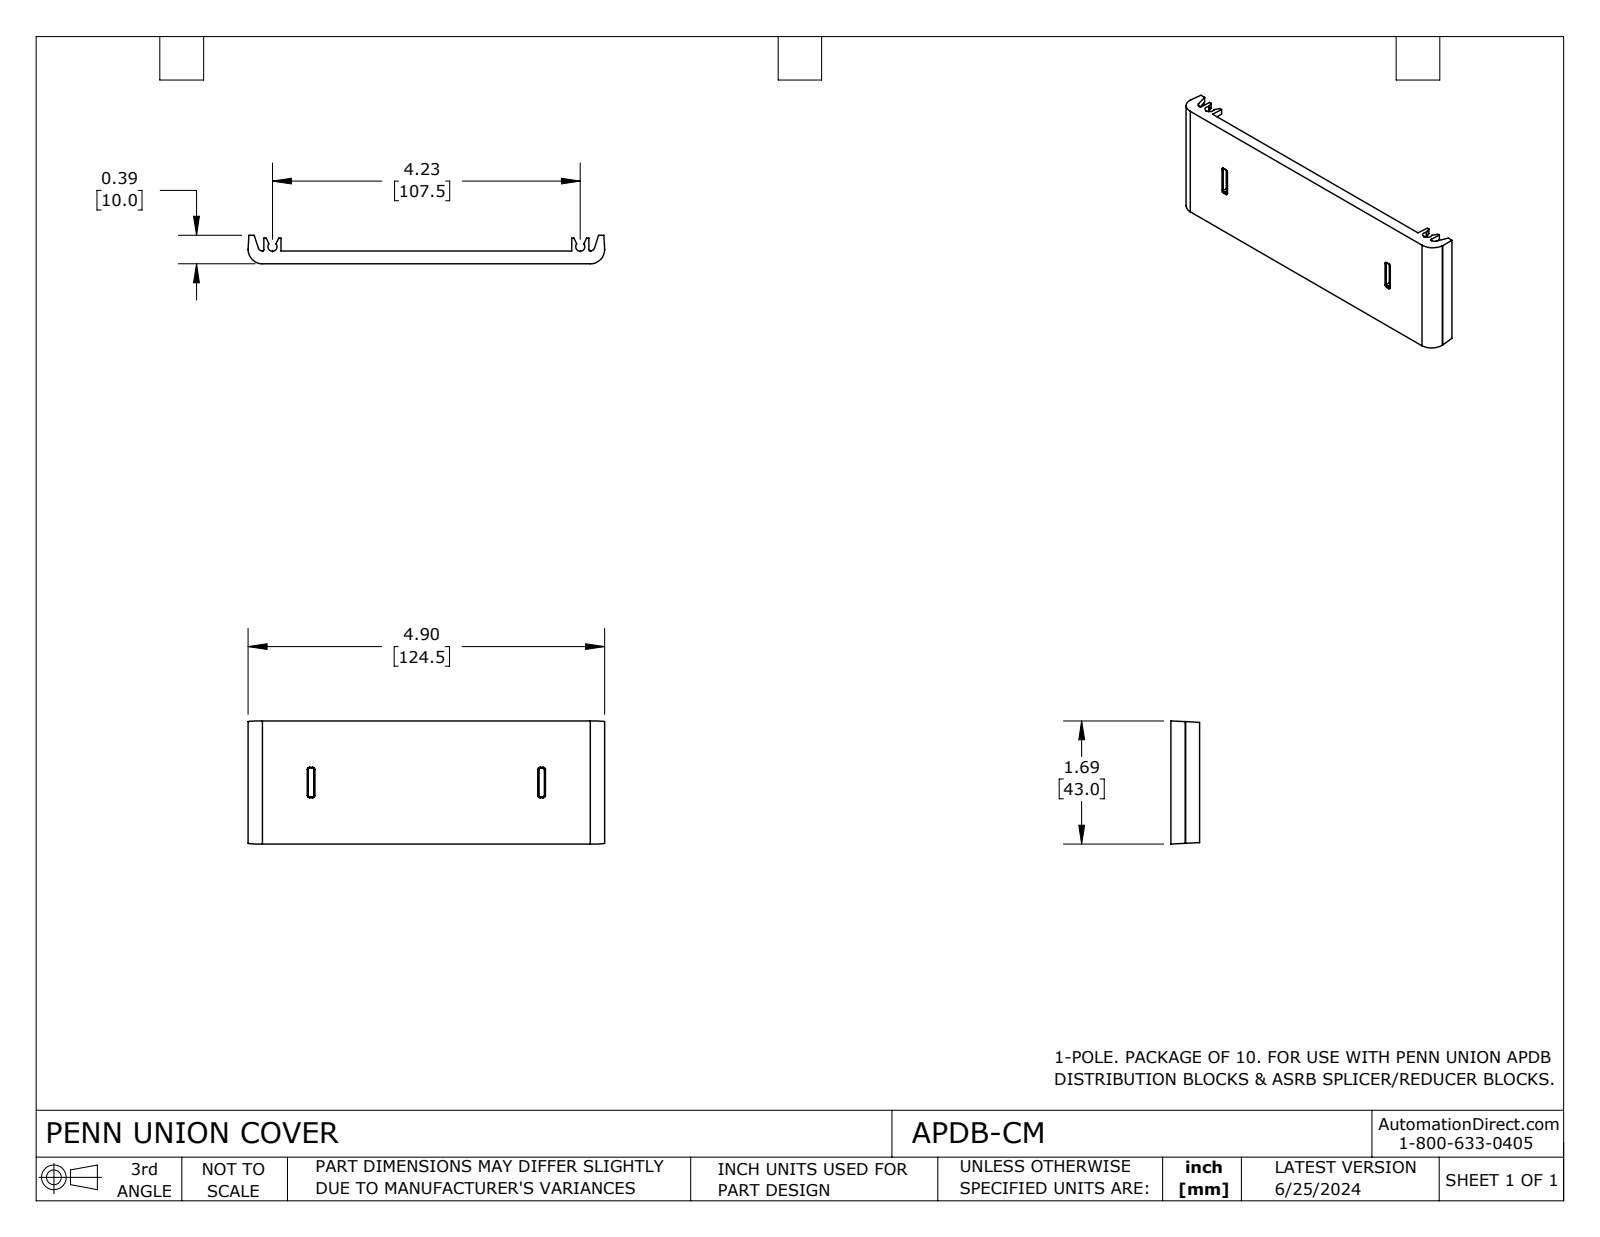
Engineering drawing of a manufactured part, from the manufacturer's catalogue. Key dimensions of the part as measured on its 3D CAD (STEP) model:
Part name (STEP PRODUCT): APDB-CM
STEP written by: SolidWorks 2023 (CONFIG_CONTROL_DESIGN)
Units: inches
Bodies: 1 solid, 120 faces (72 planar, 36 cylindrical, 12 other)
Overall size (bounding box): 4.902 × 1.693 × 0.394
Volume: 0.739 in³ · Surface area: 21.55 in²
Partial cylindrical surfaces — rounded edges, fillets, slot ends (radius × count): R0.02 ×10, R0.012 ×6, R0.059 ×2, R0.063 ×2, R0.126 ×2, R0.197 ×2
Main face-to-face distances: 0.071, 0.177, 0.106, 0.217, 0.323, 0.394, 4.232, 0.236, 3.169, 3.996
